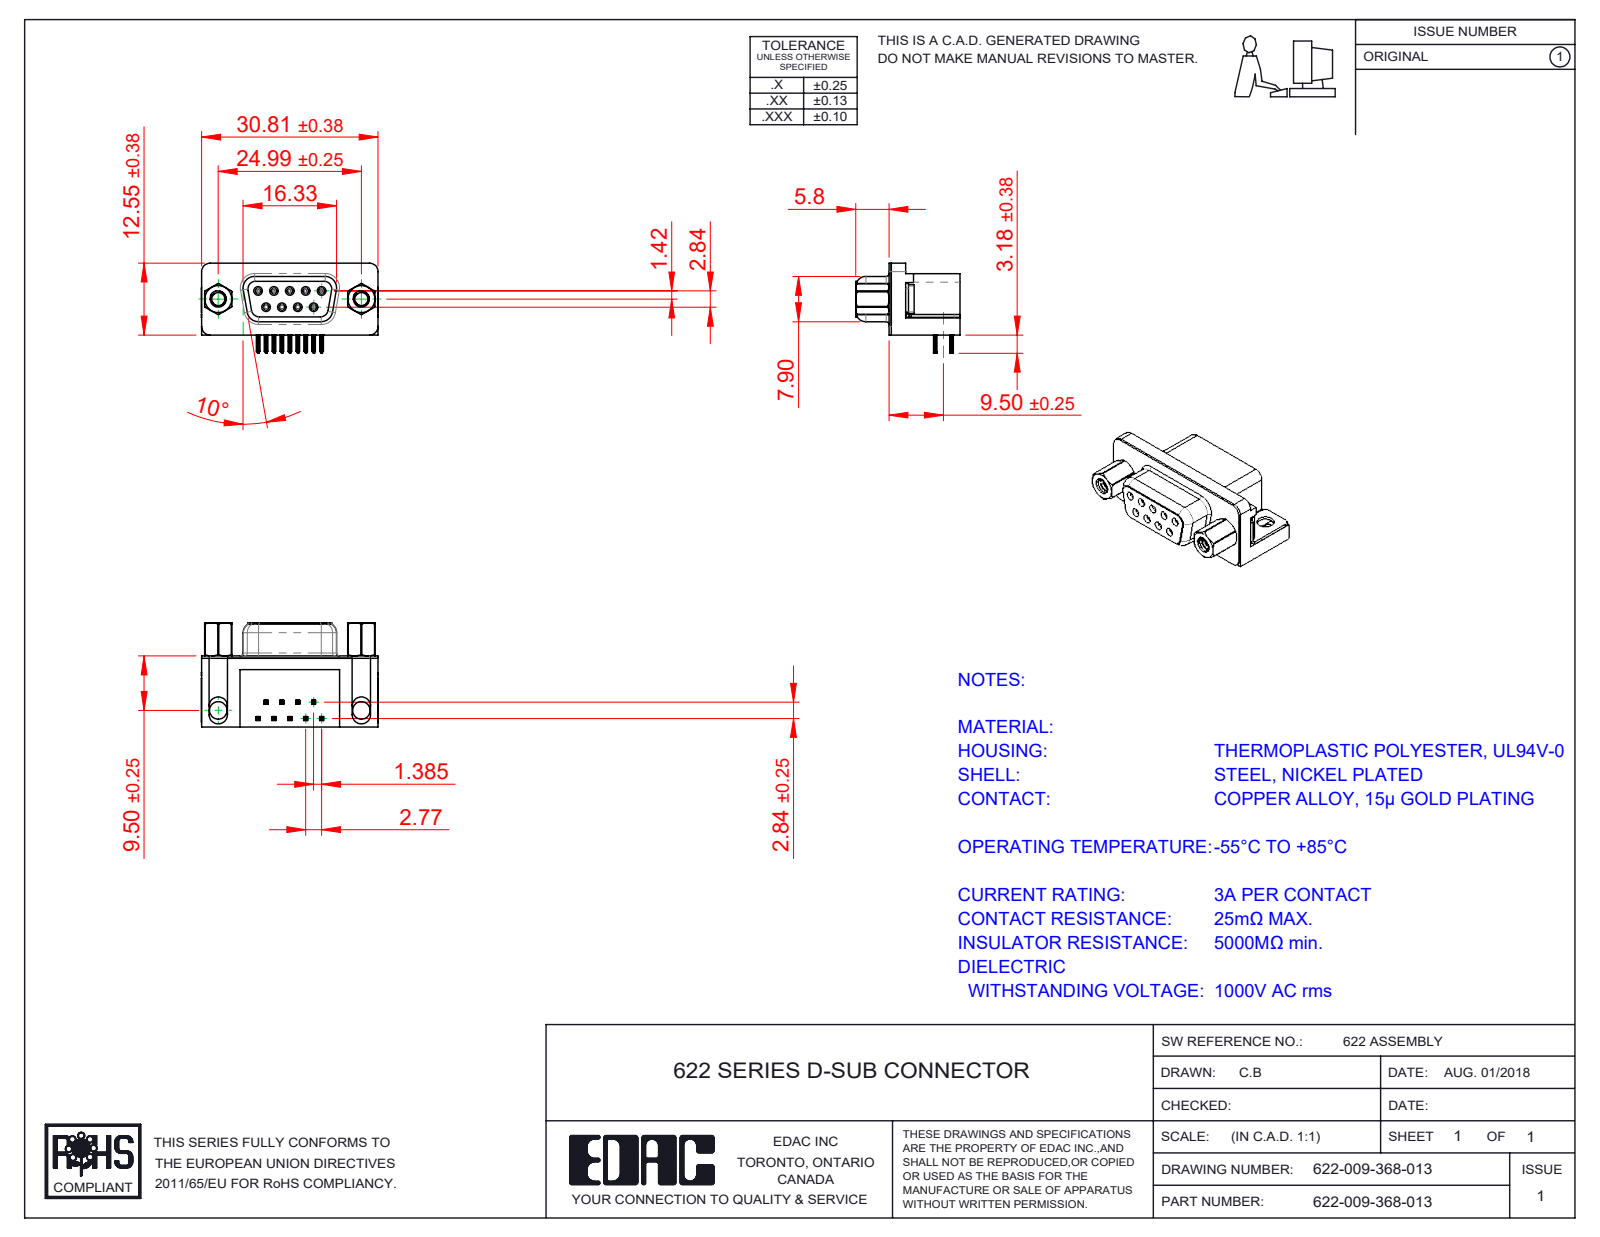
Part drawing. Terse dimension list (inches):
name: 622 Shell_9 Socket; 622 4-40 Threaded Rivet; 622 Thru Hole Board Mount; 622 Housing_9 Socket (+4 more)
written by: SolidWorks 2016 (CONFIG_CONTROL_DESIGN)
unit: in
bodies: 17 solids, 1690 faces (704 planar, 480 cylindrical, 506 other)
size: 1.216 × 0.717 × 0.619
volume: 0.24 in³; area: 8.547 in²
holes: 9× ⌀0.031, 9× ⌀0.035, 2× ⌀0.089, 2× ⌀0.09, 2× ⌀0.12, 2× ⌀0.157, 2× ⌀0.189, 2× ⌀0.197
bosses: 9× ⌀0.047, 2× ⌀0.193, 2× ⌀0.187, 2× ⌀0.154, 2× ⌀0.11
rounds: 72× R0.004, 36× R0.006, 18× R0.014, 18× R0.039, 9× R0.013, 8× R0.01, 8× R0.053, 8× R0.063
face distances: 0.016, 0.472, 0.488, 0.244, 0.014, 0.228, 0.114, 0.098, 0.407, 0.02
hole spacings: 0.124, 0.109, 0.218, 0.198, 0.198, 0.327, 0.294, 0.295
